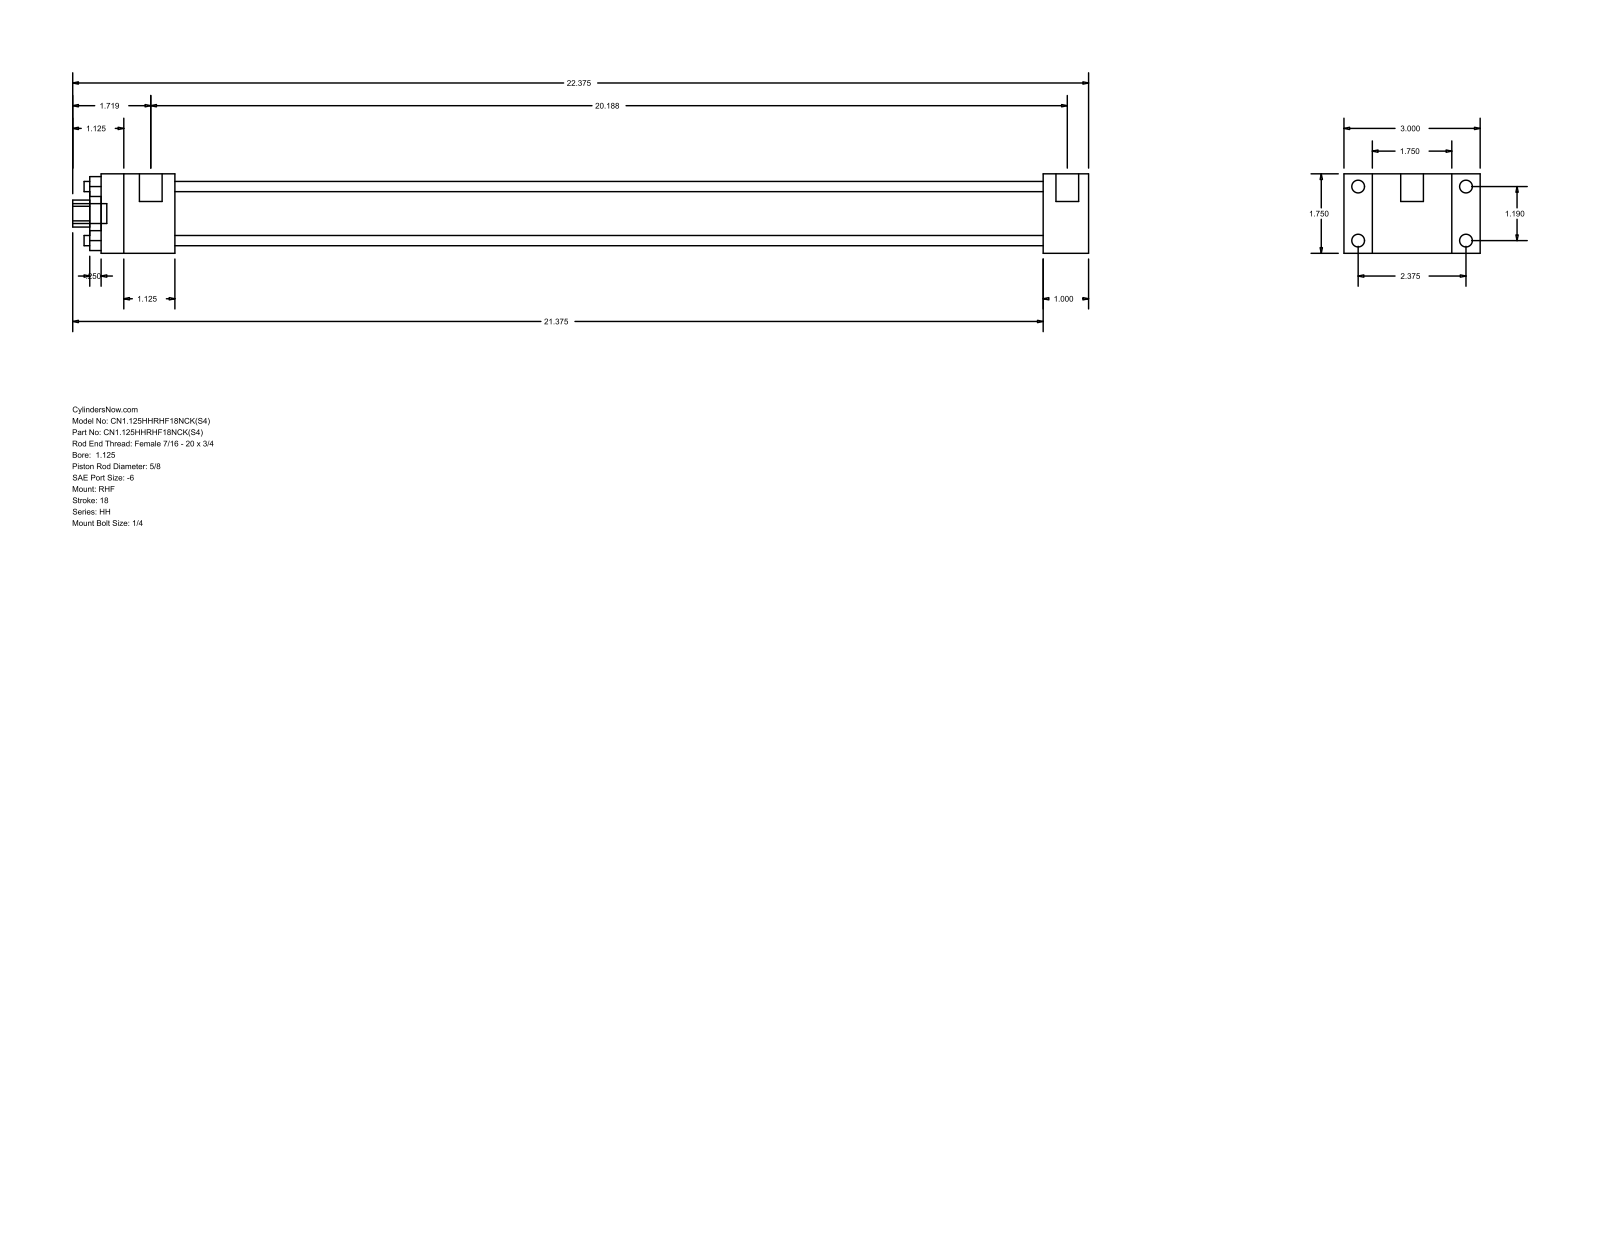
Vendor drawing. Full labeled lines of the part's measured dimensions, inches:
Part name (STEP PRODUCT): HH_RHF__0112_0.625
STEP written by: GSSL Pune (CONFIG_CONTROL_DESIGN)
Units: inches
Bodies: 0 solids, 88 faces (60 planar, 28 cylindrical, 0 other)
Overall size (bounding box): 22.375 × 3 × 1.75
Round holes (diameter × count): ⌀0.225 ×4, ⌀0.625 ×1, ⌀1.125 ×1, ⌀1.375 ×1
Round bosses / shafts (diameter × count): ⌀0.281 ×4, ⌀0.219 ×4, ⌀0.5 ×2, ⌀0.437 ×1
Partial cylindrical surfaces — rounded edges, fillets, slot ends (radius × count): R0.297 ×1
Main face-to-face distances: 1.75, 0.625, 2.375, 1, 3, 19.125, 20.125, 1.625, 20.75, 21.75
Hole centre spacings: 0.841, 1.19, 1.683
